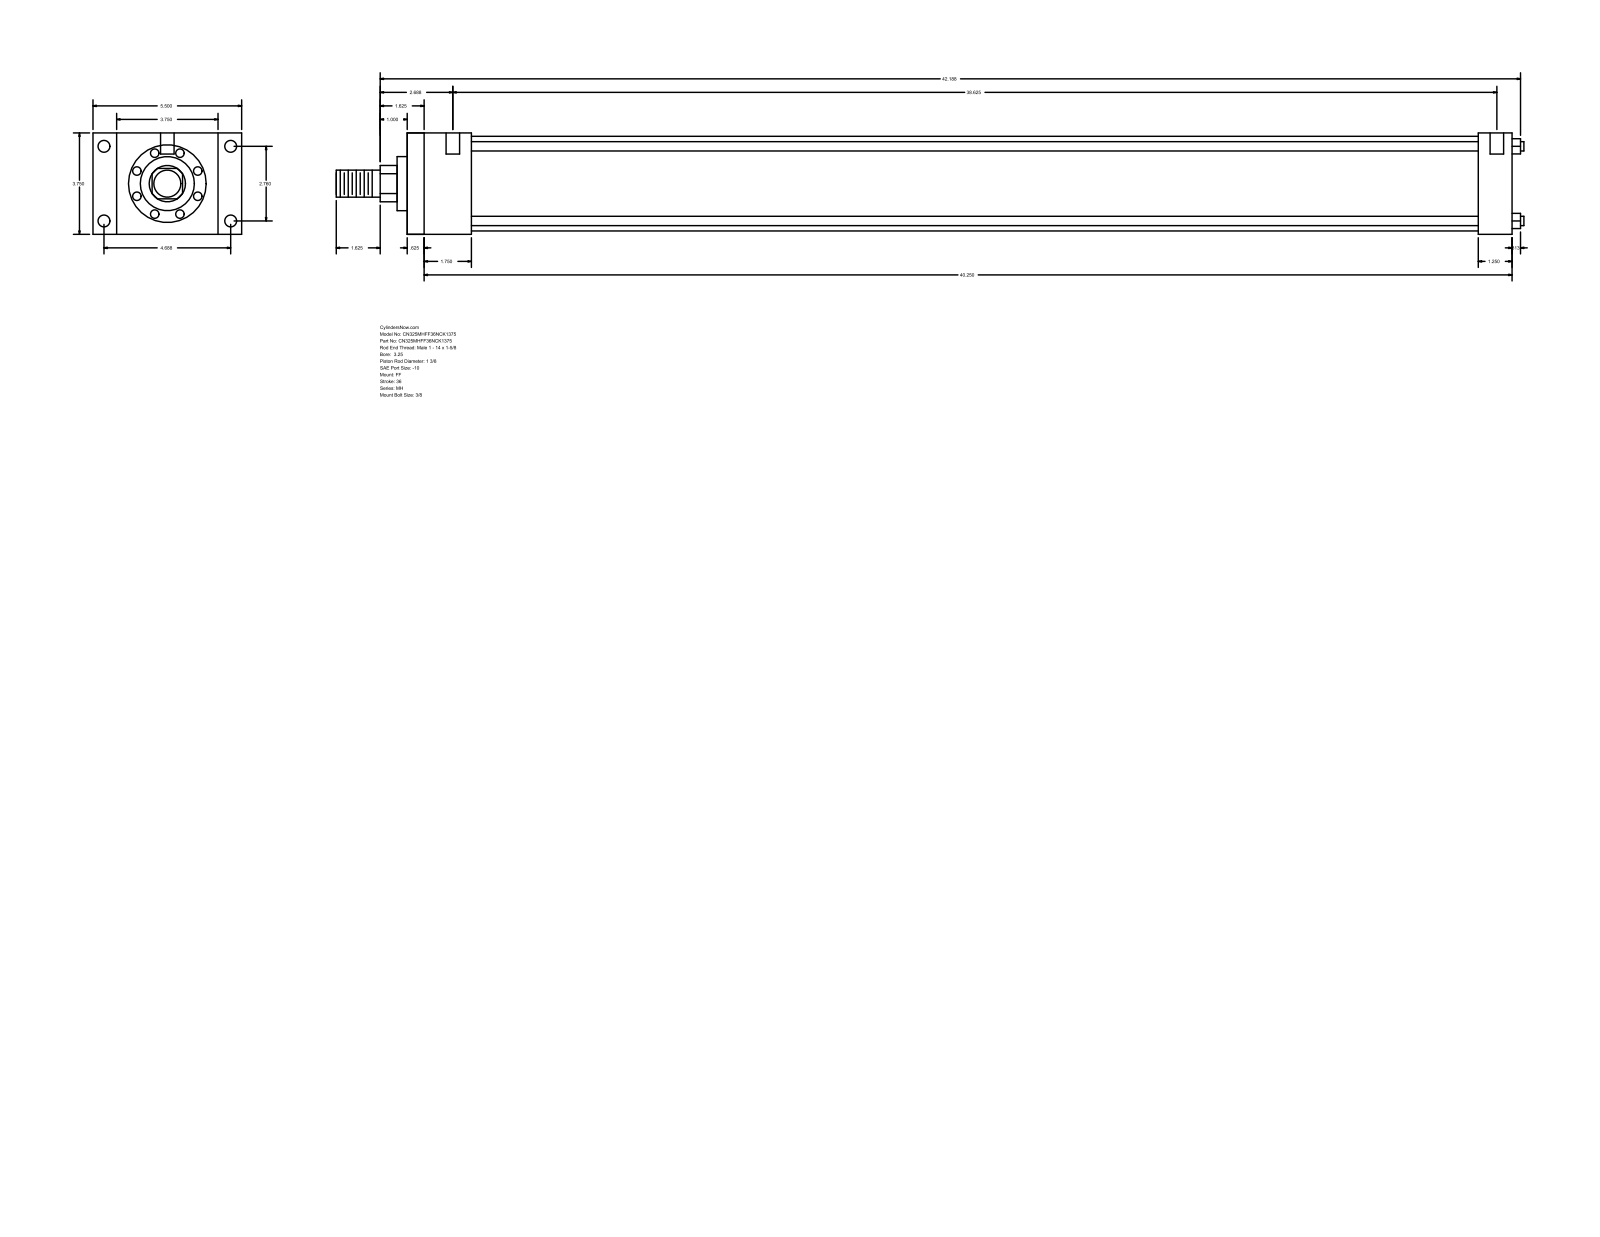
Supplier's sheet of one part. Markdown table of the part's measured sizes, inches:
| quantity | value |
| --- | --- |
| part name | MH_FF__0325_1.375 |
| STEP written by | GSSL Pune (CONFIG_CONTROL_DESIGN) |
| units | inches |
| bodies | 0 solids, 92 faces (64 planar, 28 cylindrical, 0 other) |
| overall size | 43.937 × 5.5 × 3.75 |
| round holes (diameter × count) | 0.219 × 4, 0.438 × 4, 0.5 × 2 |
| round bosses / shafts (diameter × count) | 0.345 × 4, 3.5 × 1, 2 × 1, 1.375 × 1, 1 × 1 |
| partial cylindrical surfaces (radius × count) | 0.672 × 1 |
| main face-to-face distances | 3.75, 40.875, 0.625, 40.25, 0.875, 4.625, 39.625, 39, 1.25, 2.375 |
| hole center spacings | 2.76, 4.687, 5.439, 38.875, 0.063, 0.187, 38.625, 38.688 |
